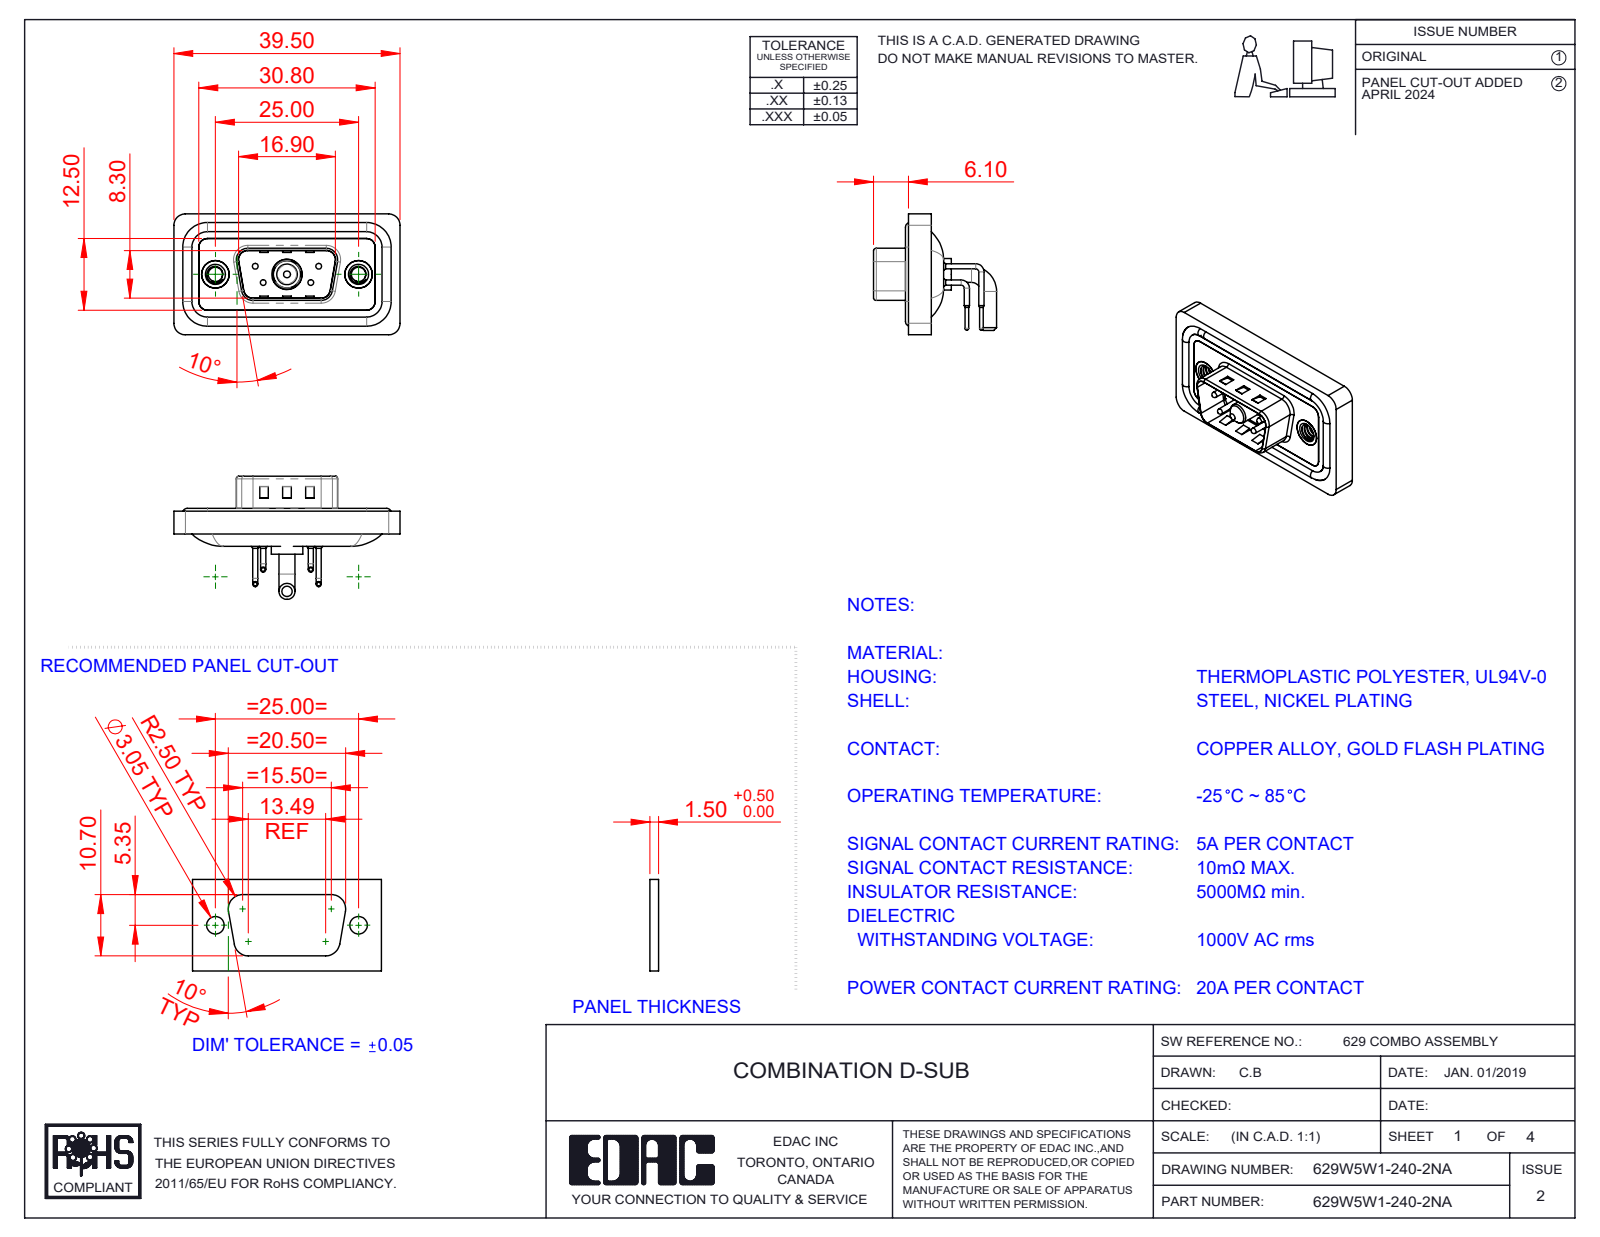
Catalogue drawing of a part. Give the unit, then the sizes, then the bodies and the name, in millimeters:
Units: millimetres
Overall size (bounding box): 39.5 × 21.5 × 21.1
Round holes (diameter × count): ⌀0.75 ×4, ⌀1.6 ×4, ⌀2 ×4, ⌀2.5 ×2, ⌀4 ×2, ⌀4.8 ×2, ⌀5 ×2, ⌀4.85 ×1, ⌀5.3 ×1
Round bosses / shafts (diameter × count): ⌀0.9 ×8, ⌀1.6 ×4, ⌀1.5 ×4, ⌀1 ×4, ⌀0.65 ×4, ⌀4.9 ×2, ⌀2.8 ×2, ⌀5.5 ×1
Partial cylindrical surfaces — rounded edges, fillets, slot ends (radius × count): R1.5 ×18, R2 ×18, R0.5 ×8, R1.6 ×8, R0.25 ×4, R0.6 ×4, R0.65 ×4, R0.9 ×4
Main face-to-face distances: 0.4, 2.9, 1.1, 0.8, 2.1, 2.5, 1.6, 3.1, 4.5, 1.5
Hole centre spacings: 3.16, 5.72, 7.1, 12.5, 18.1, 4.39, 4.4, 8.31
Volume: 4 479 mm³ · Surface area: 7 167 mm²
Bodies: 13 solids, 888 faces (411 planar, 343 cylindrical, 134 other)
Part name (STEP PRODUCT): 629Combo Contact Row 1; 629Combo Threaded Rivet_A; 629Combo Shell Rear_09 Contacts; 629Combo Housing_5W1 (+5 more)
STEP written by: SolidWorks 2023 (CONFIG_CONTROL_DESIGN)
